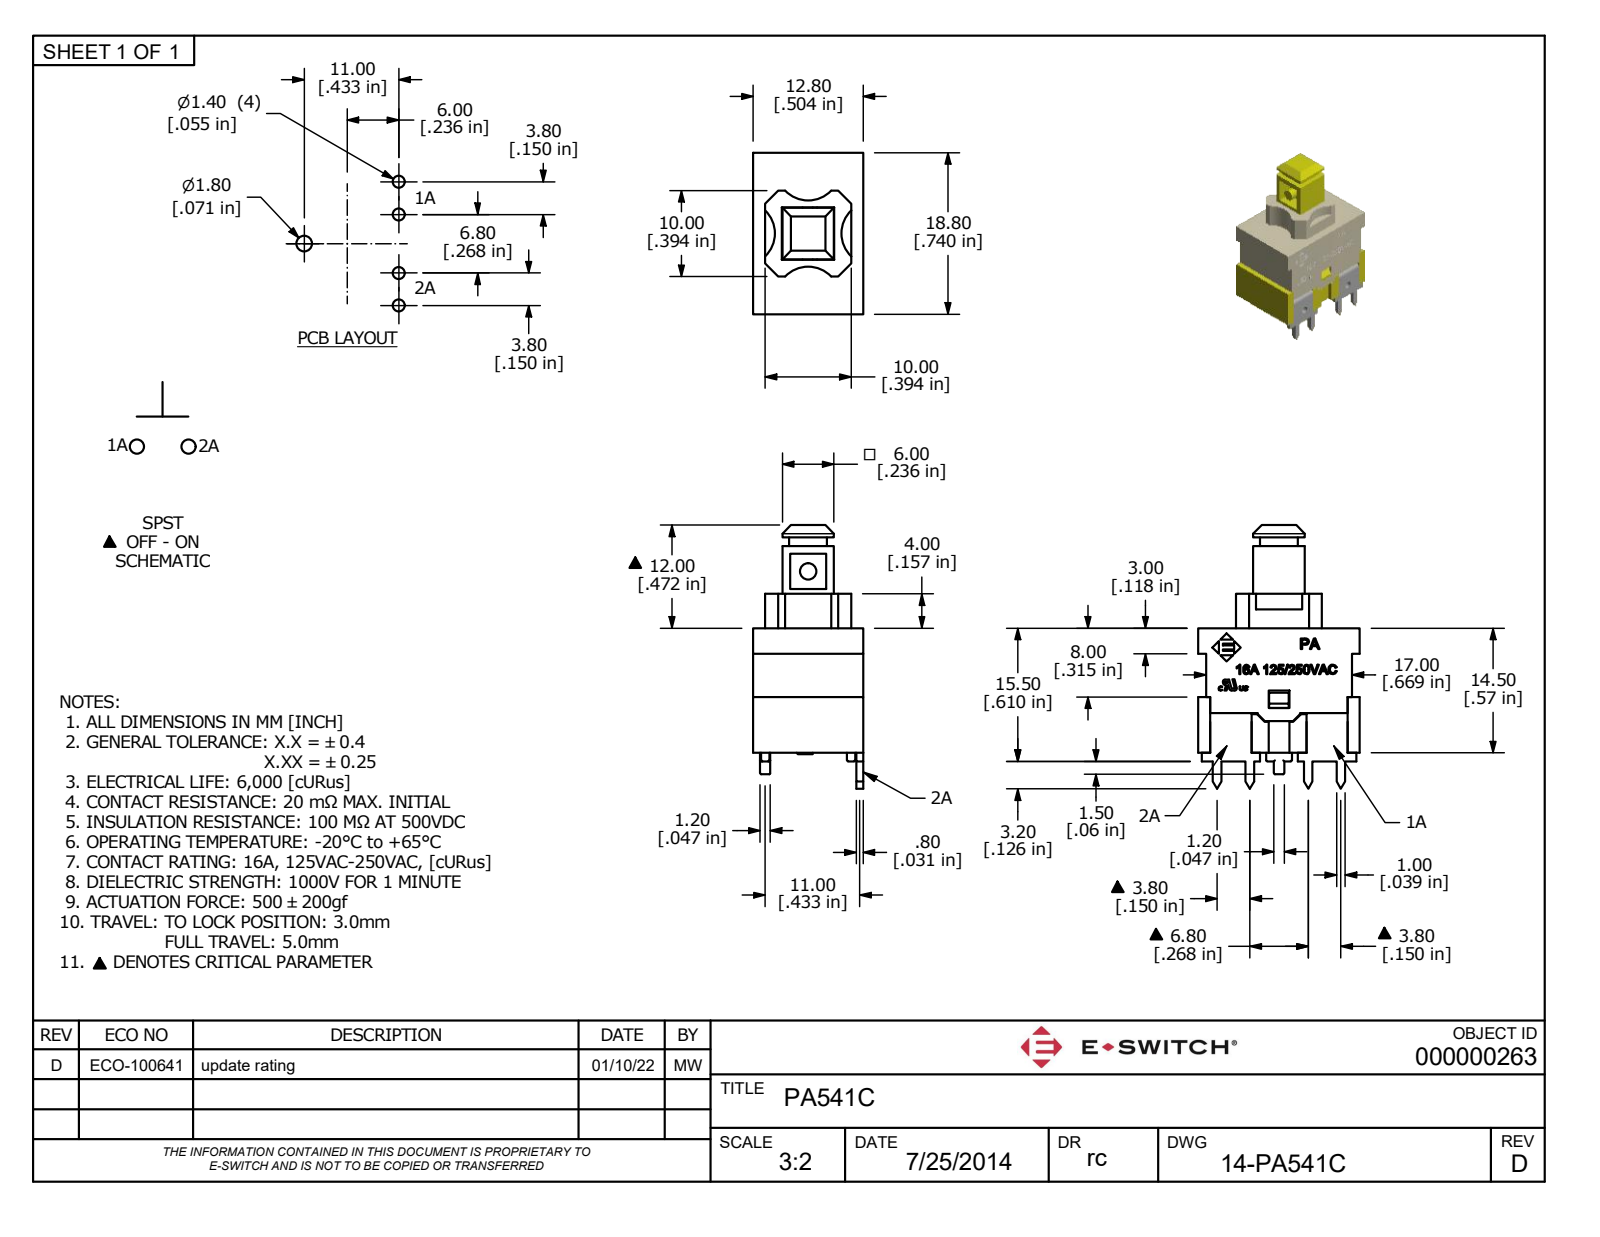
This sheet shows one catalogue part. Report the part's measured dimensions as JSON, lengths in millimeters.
{"part_name": "14-PA541C; P4-P5 Base; Terminal_4_NO; Terminal_4_COM (+2 more)", "step_written_by": "Autodesk Inventor 2018 (AP242_MANAGED_MODEL_BASED_3D_ENGINEERING_MIM_LF)", "units": "millimeters", "bodies": {"solids": 5, "faces": 1133, "planar": 815, "cylindrical": 58, "other": 260}, "overall_size": [30.9, 18.8, 12.8], "volume_mm3": 2106, "surface_area_mm2": 4558, "round_holes": [[3, 1]], "round_bosses_or_shafts": [[0.95, 4], [2.5, 1], [1.9, 1]], "partial_cylinders_radius": [[0.25, 22], [0.15, 8], [0.1, 6], [3.71, 4], [0.29, 3], [1, 2], [0.5, 1], [1.79, 1]], "face_to_face_distances": [0.75, 11.95, 0.8, 16.8, 0.9, 11.2, 2, 1.7, 4.2, 6.85]}
